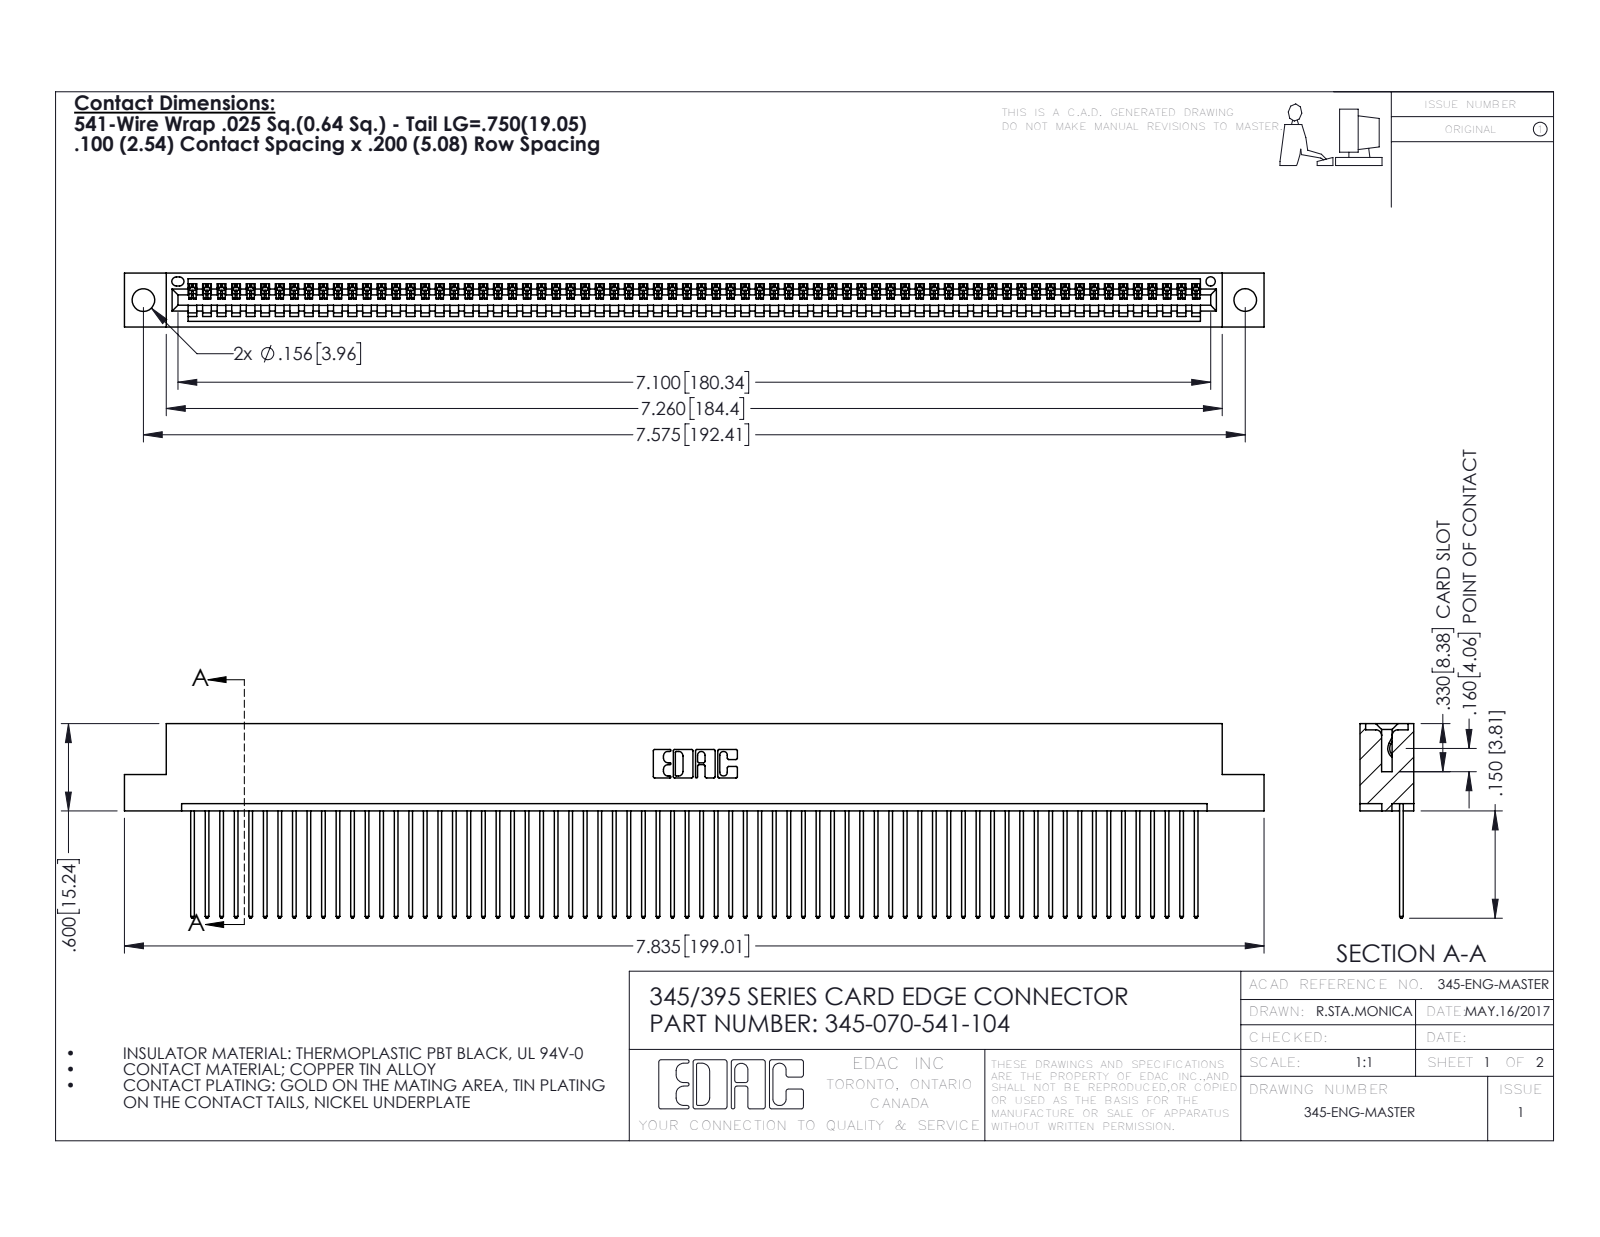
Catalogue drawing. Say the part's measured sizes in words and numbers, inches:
The part is named "345-292-001_345-293-141; 345-070-541-104; 345 Part_Flush Mounting Lugs - 0.156 Dia-TH". Its 3-D file was written by "SolidWorks 2016 (CONFIG_CONTROL_DESIGN)". It is 71 solids with 4186 faces: 2880 planar, 1306 cylindrical and 0 other. Overall it measures 7.835 by 1.337 by 0.37 inches. Its volume is 1.176 cubic inches and its surface area 42.1 square inches. Round holes: 2 of diameter 0.156, 1 of diameter 0.064. Partial cylindrical surfaces (rounded edges, fillets, slot ends): 140 of radius 0.006, 140 of radius 0.01, 22 of radius 0.01, 6 of radius 0.007, 6 of radius 0.031, 3 of radius 0.026, 2 of radius 0.031, 2 of radius 0.04. The main face-to-face distances are 0.072, 0.298, 0.098, 0.272, 0.025, 0.37, 0.2, 0.225, 0.149, 0.072. The hole center spacings are 0.27, 7.339, 7.575.
